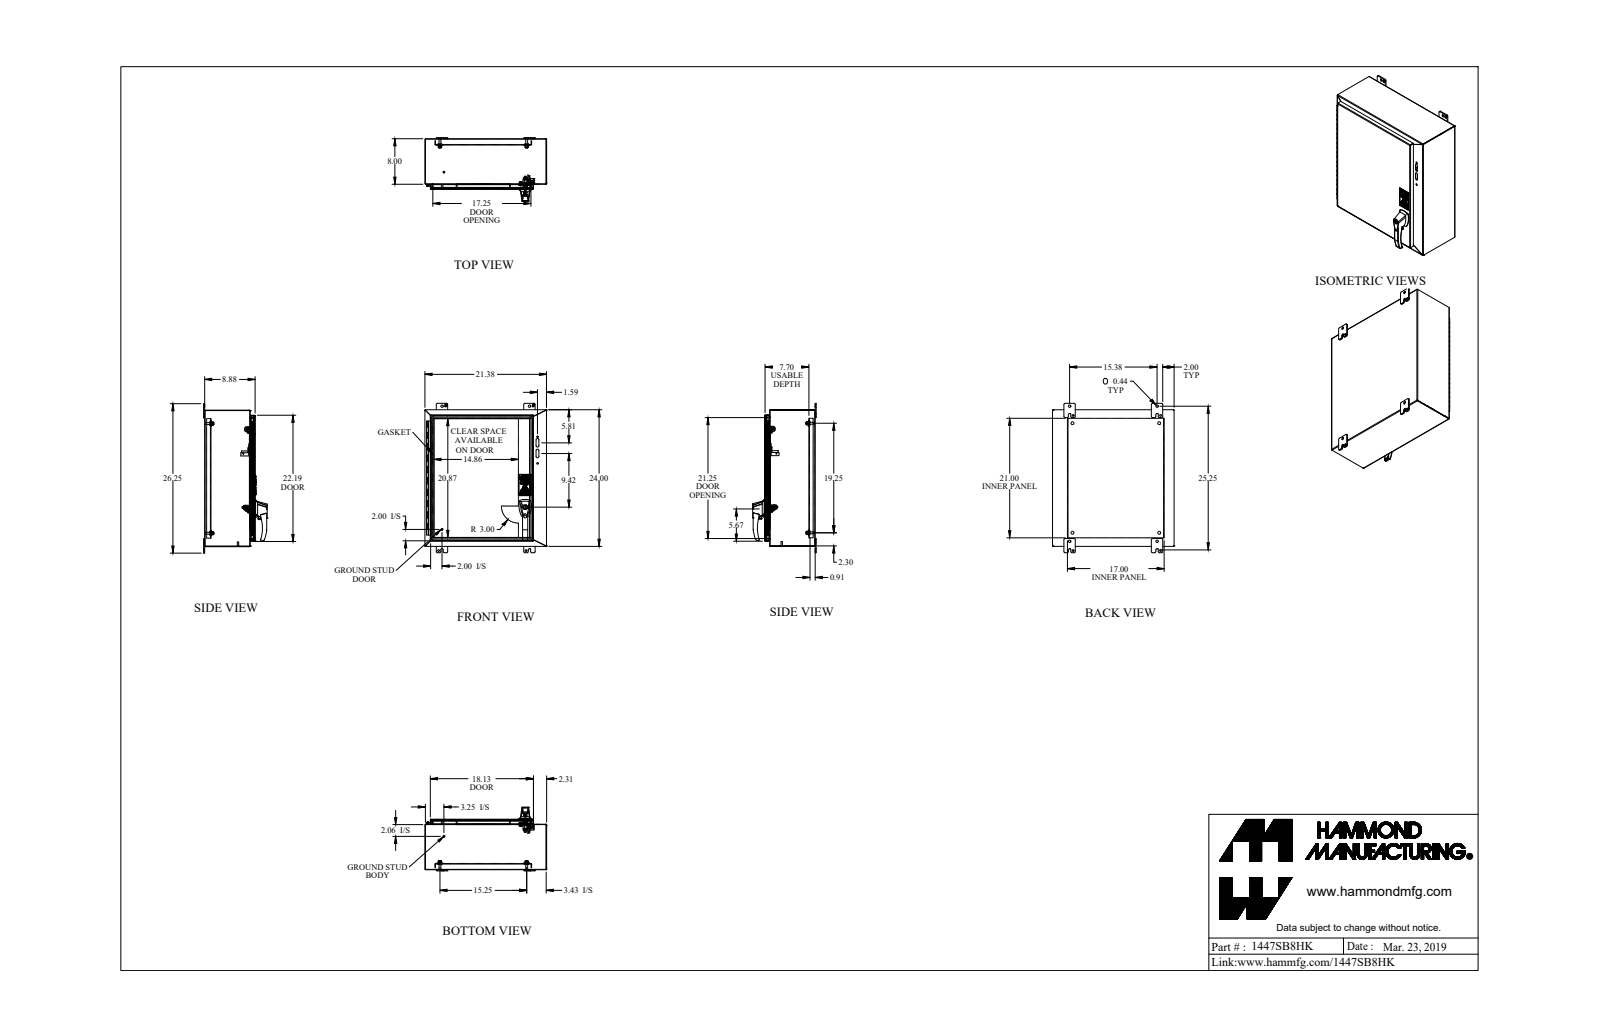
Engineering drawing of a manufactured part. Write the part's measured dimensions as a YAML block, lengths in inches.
part_name: "1447SB8HK"
step_written_by: "SolidWorks 2019 (AUTOMOTIVE_DESIGN)"
units: inches
bodies: {solids: 49, faces: 1210, planar: 754, cylindrical: 333, other: 123}
overall_size: [26.25, 21.375, 11.177]
volume: 201.5
surface_area: 5013
round_holes:
  - {diameter: 0.313, count: 5}
  - {diameter: 0.176, count: 4}
  - {diameter: 0.437, count: 4}
  - {diameter: 0.5, count: 4}
  - {diameter: 0.156, count: 2}
  - {diameter: 0.173, count: 2}
  - {diameter: 0.215, count: 2}
  - {diameter: 0.25, count: 2}
  - {diameter: 0.265, count: 2}
  - {diameter: 0.281, count: 2}
  - {diameter: 0.307, count: 2}
  - {diameter: 0.413, count: 2}
round_bosses_or_shafts:
  - {diameter: 0.375, count: 8}
  - {diameter: 0.25, count: 7}
  - {diameter: 1, count: 4}
  - {diameter: 0.65, count: 4}
  - {diameter: 0.33, count: 4}
  - {diameter: 0.156, count: 4}
  - {diameter: 0.5, count: 2}
  - {diameter: 0.402, count: 2}
partial_cylinders:
  - {radius: 0.188, count: 24}
  - {radius: 0.25, count: 24}
  - {radius: 0.036, count: 20}
  - {radius: 0.108, count: 20}
  - {radius: 0.125, count: 11}
  - {radius: 0.03, count: 8}
  - {radius: 0.218, count: 8}
  - {radius: 0.06, count: 7}
face_to_face_distances: [0.072, 8.803, 8.731, 8.875, 0.095, 21.303, 7.771, 7.699, 1.032, 1.104]
hole_center_spacings: [15.25, 15.375, 1.111, 14.674, 24.559, 1.735, 1.736, 1.855]
